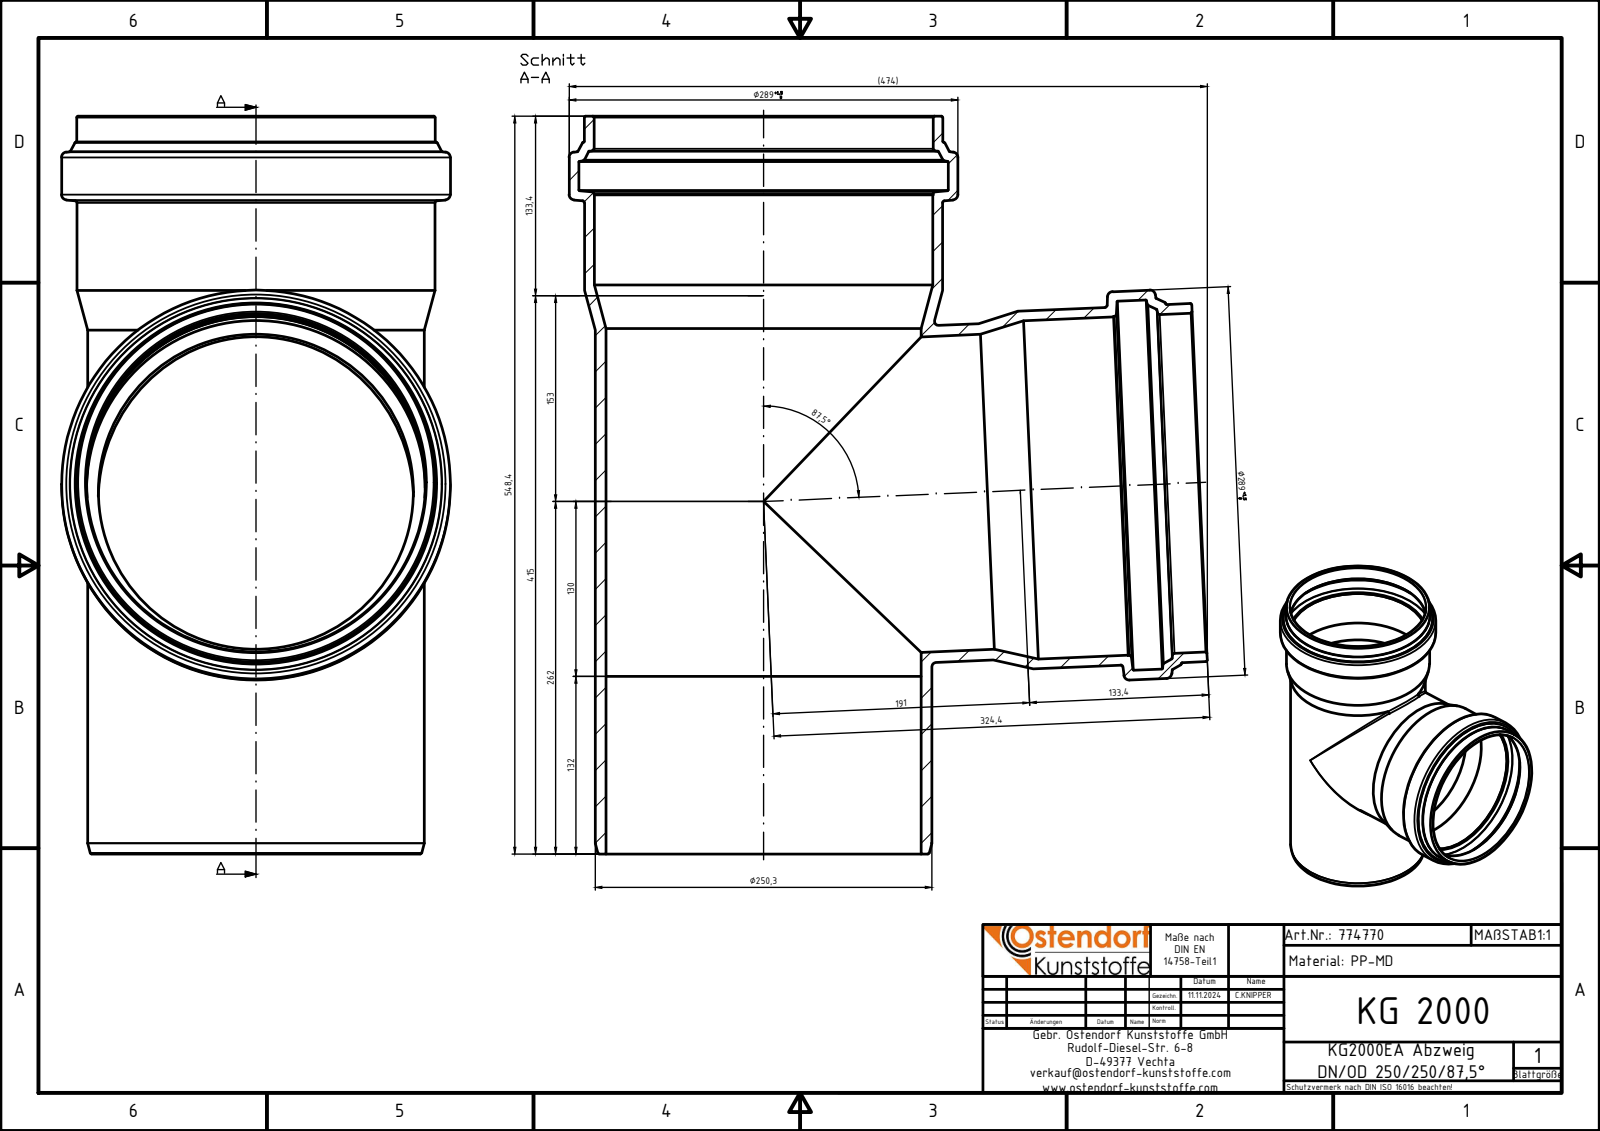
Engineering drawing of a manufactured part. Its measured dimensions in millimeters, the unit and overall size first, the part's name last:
Units: millimetres
Overall size (bounding box): 548.4 × 474.36 × 289
Round holes (diameter × count): ⌀252.1 ×3, ⌀234.3 ×2, ⌀251.7 ×2, ⌀274.6 ×2
Round bosses / shafts (diameter × count): ⌀289 ×2, ⌀266.5 ×2, ⌀266.1 ×2, ⌀250.3 ×2
Main face-to-face distances: 548.4, 58.5, 489.9
Volume: 4 579 000 mm³ · Surface area: 1 203 000 mm²
Bodies: 1 solid, 78 faces (5 planar, 18 cylindrical, 55 other)
Part name (STEP PRODUCT): 774770z
STEP written by: Autodesk Inventor 2024 (AUTOMOTIVE_DESIGN)
